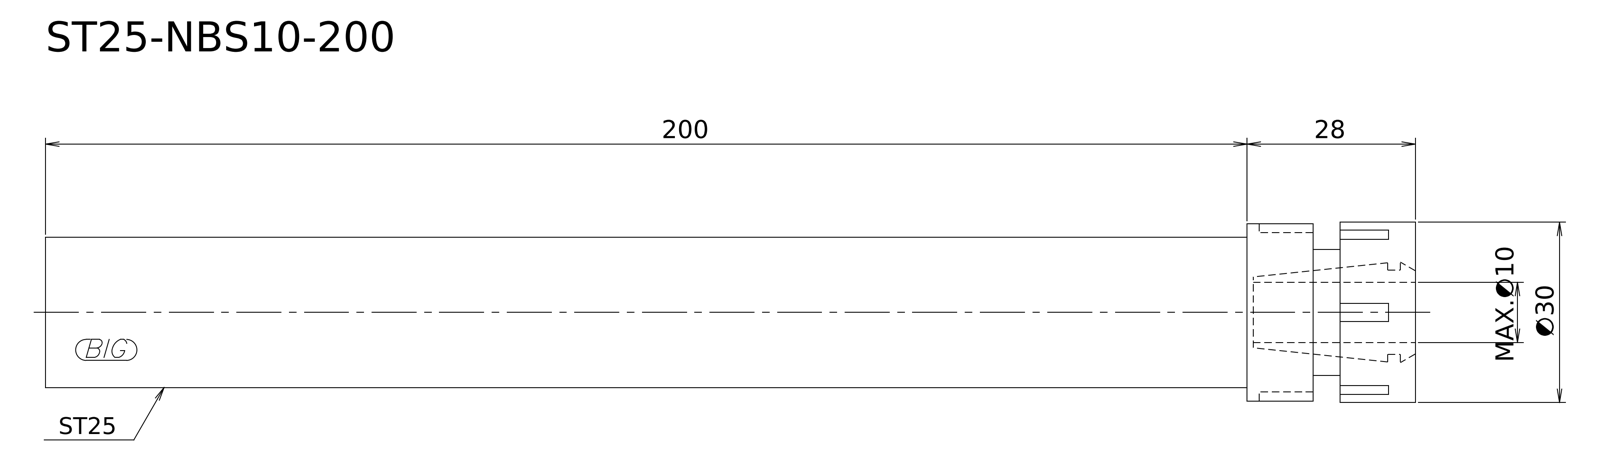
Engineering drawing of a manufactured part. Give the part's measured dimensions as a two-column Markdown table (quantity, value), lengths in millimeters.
| quantity | value |
| --- | --- |
| STEP written by | Kubotek KeyCreator V8.5.1 (14335) (CONFIG_CONTROL_DESIGN) |
| units | millimeters |
| bodies | 1 solid, 9 faces (5 planar, 4 cylindrical, 0 other) |
| overall size | 228 × 30 × 30 |
| volume | 116 088 mm³ |
| surface area | 20 290 mm² |
| round bosses / shafts (diameter × count) | 30 × 1, 29.5 × 1, 25 × 1, 21 × 1 |
| main face-to-face distances | 228, 12.5, 215.5, 17, 4.5, 211, 28, 15.5, 11, 200 |
